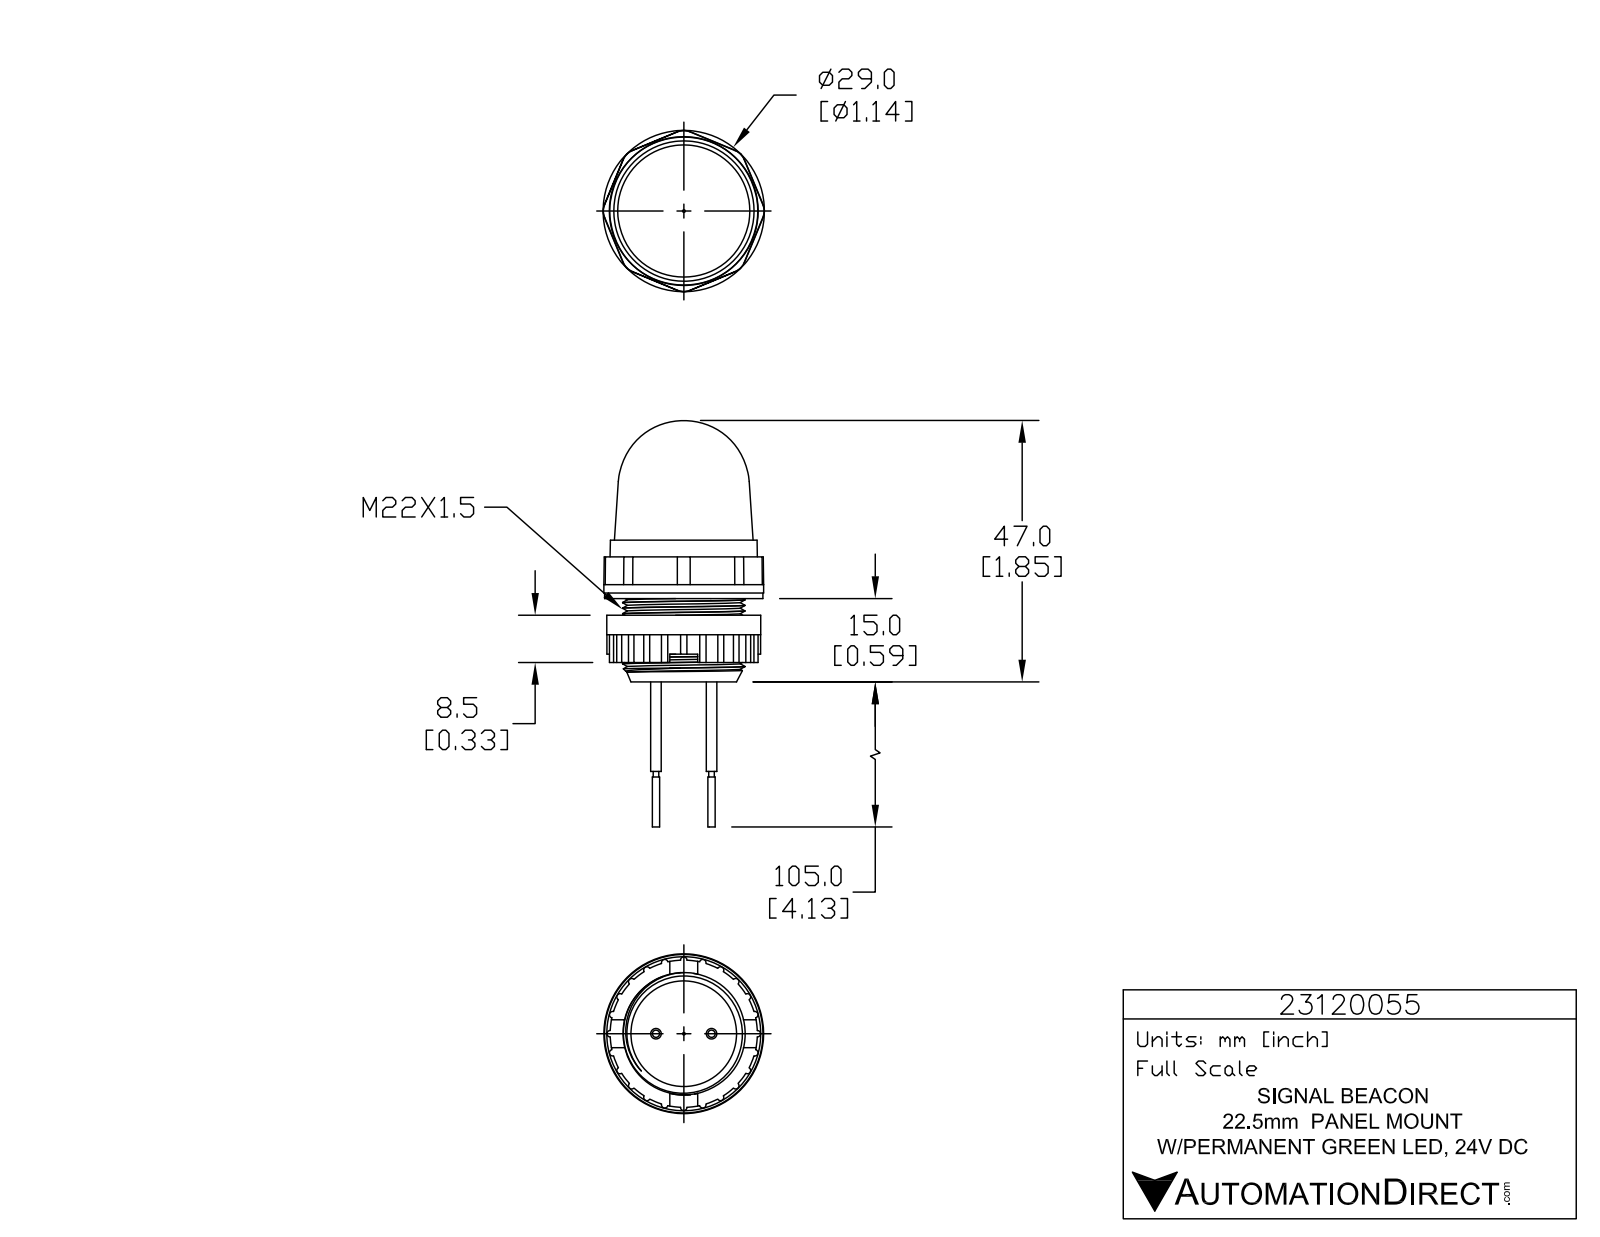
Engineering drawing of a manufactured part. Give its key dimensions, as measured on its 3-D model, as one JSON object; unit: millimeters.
{"part_name": "23120055", "step_written_by": "SolidWorks 2017 (AUTOMOTIVE_DESIGN)", "units": "millimeters", "bodies": {"solids": 1, "faces": 934, "planar": 568, "cylindrical": 269, "other": 97}, "overall_size": [71.6, 28.7, 28.7], "volume_mm3": 20570, "surface_area_mm2": 7845, "round_holes": [[0.5, 3]], "round_bosses_or_shafts": [[2.9, 3], [0.7, 3], [1.9, 2], [1.3, 2], [1, 2], [28.7, 1], [28.5, 1], [27.7, 1]], "partial_cylinders_radius": [[0.6, 24], [3, 8], [0.1, 6], [0.1, 6], [0.1, 6], [1.7, 6], [0.1, 3], [0.2, 3]], "face_to_face_distances": [14, 3, 11, 2.5, 8.5, 11.5, 12.5, 10.5, 7.5, 5]}
